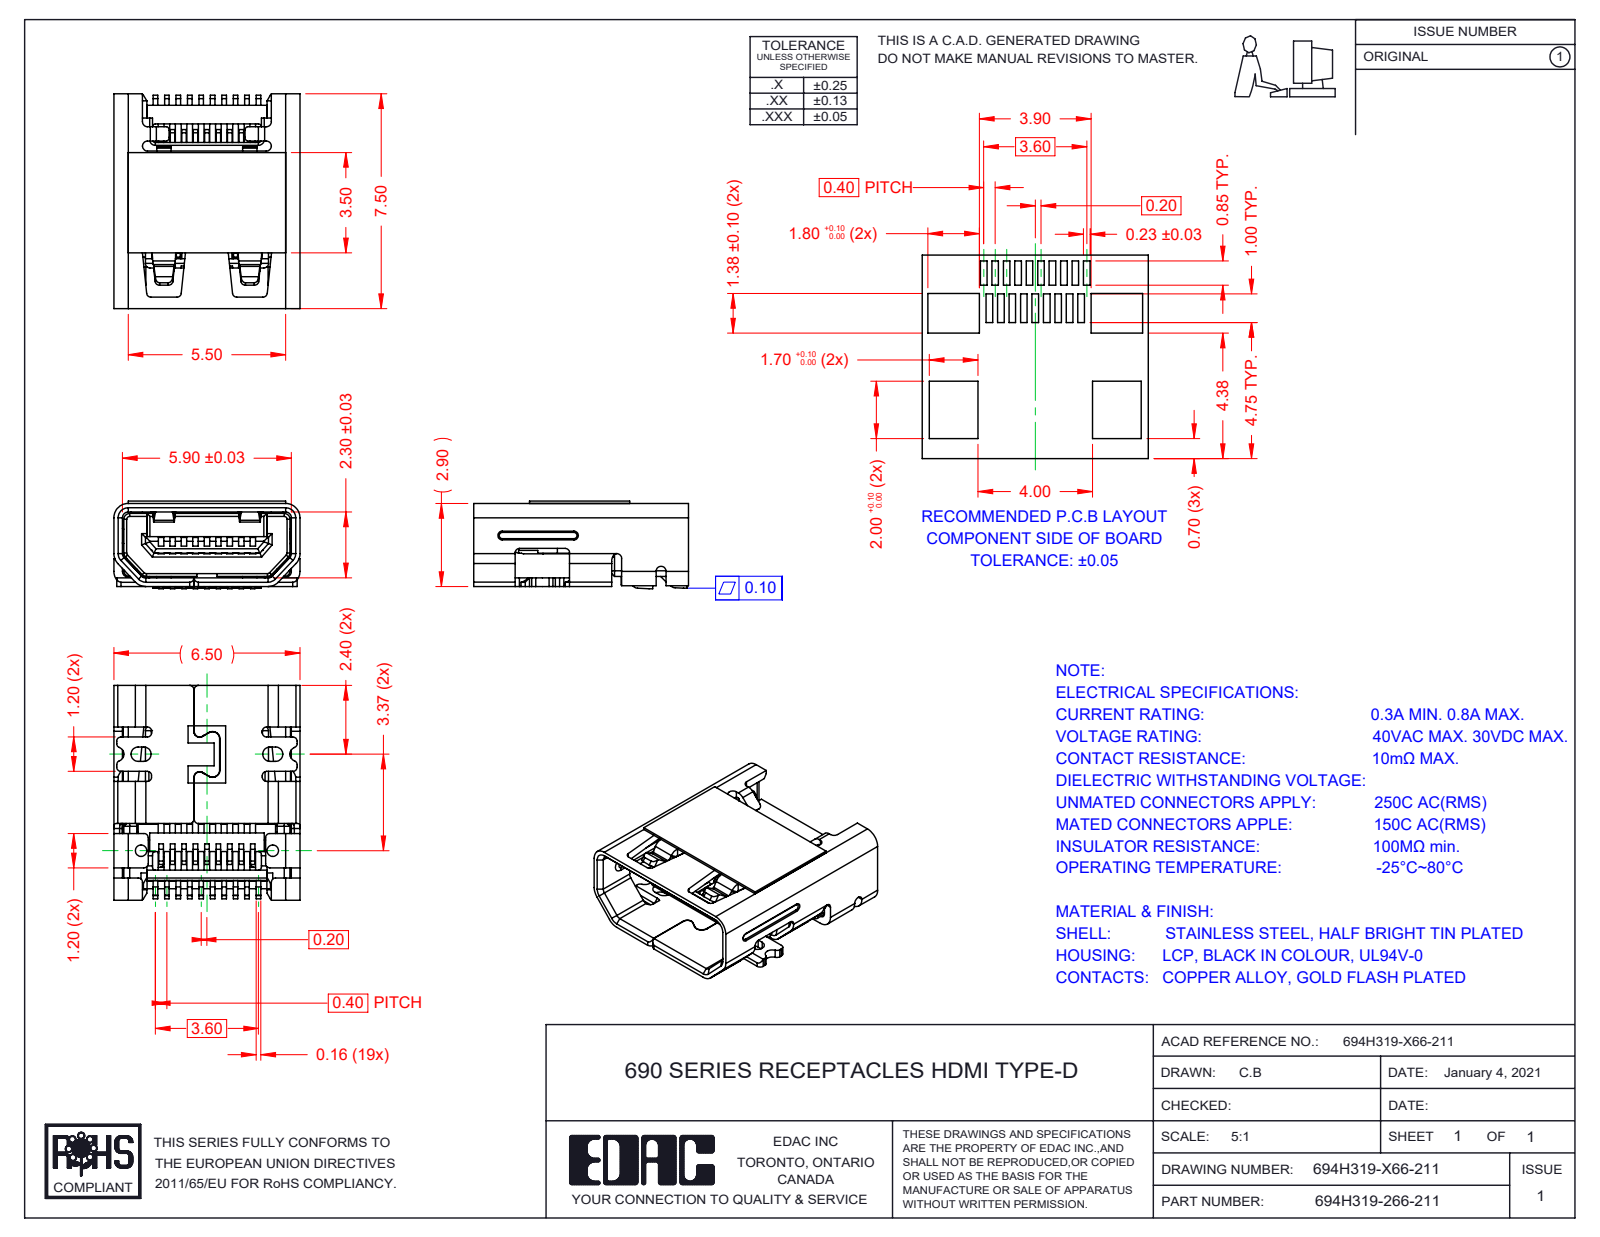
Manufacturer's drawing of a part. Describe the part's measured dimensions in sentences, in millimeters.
The part is named "694H319-166-211; Shell 694H319-X66-211; Tape 694H319-X66-211; Insulator 694H319-X66-211". Its 3-D file was written by "SolidWorks 2020 (AUTOMOTIVE_DESIGN)". It is 3 solids with 1385 faces: 1104 planar, 221 cylindrical and 60 other. Overall it measures 7.5 by 6.5 by 3.06 millimeters. Its volume is 62 cubic millimeters and its surface area 457 square millimeters. Round holes: 2 of diameter 0.4. Partial cylindrical surfaces (rounded edges, fillets, slot ends): 47 of radius 0.15, 18 of radius 0.2, 8 of radius 0.25, 8 of radius 0.5, 6 of radius 0.16, 6 of radius 0.17, 6 of radius 0.35, 4 of radius 0.1. The main face-to-face distances are 2.6, 2.3, 2.9, 0.35, 2.68, 0.38, 0.65, 2.98, 6.2, 0.5. The hole center spacings are 4.6.
